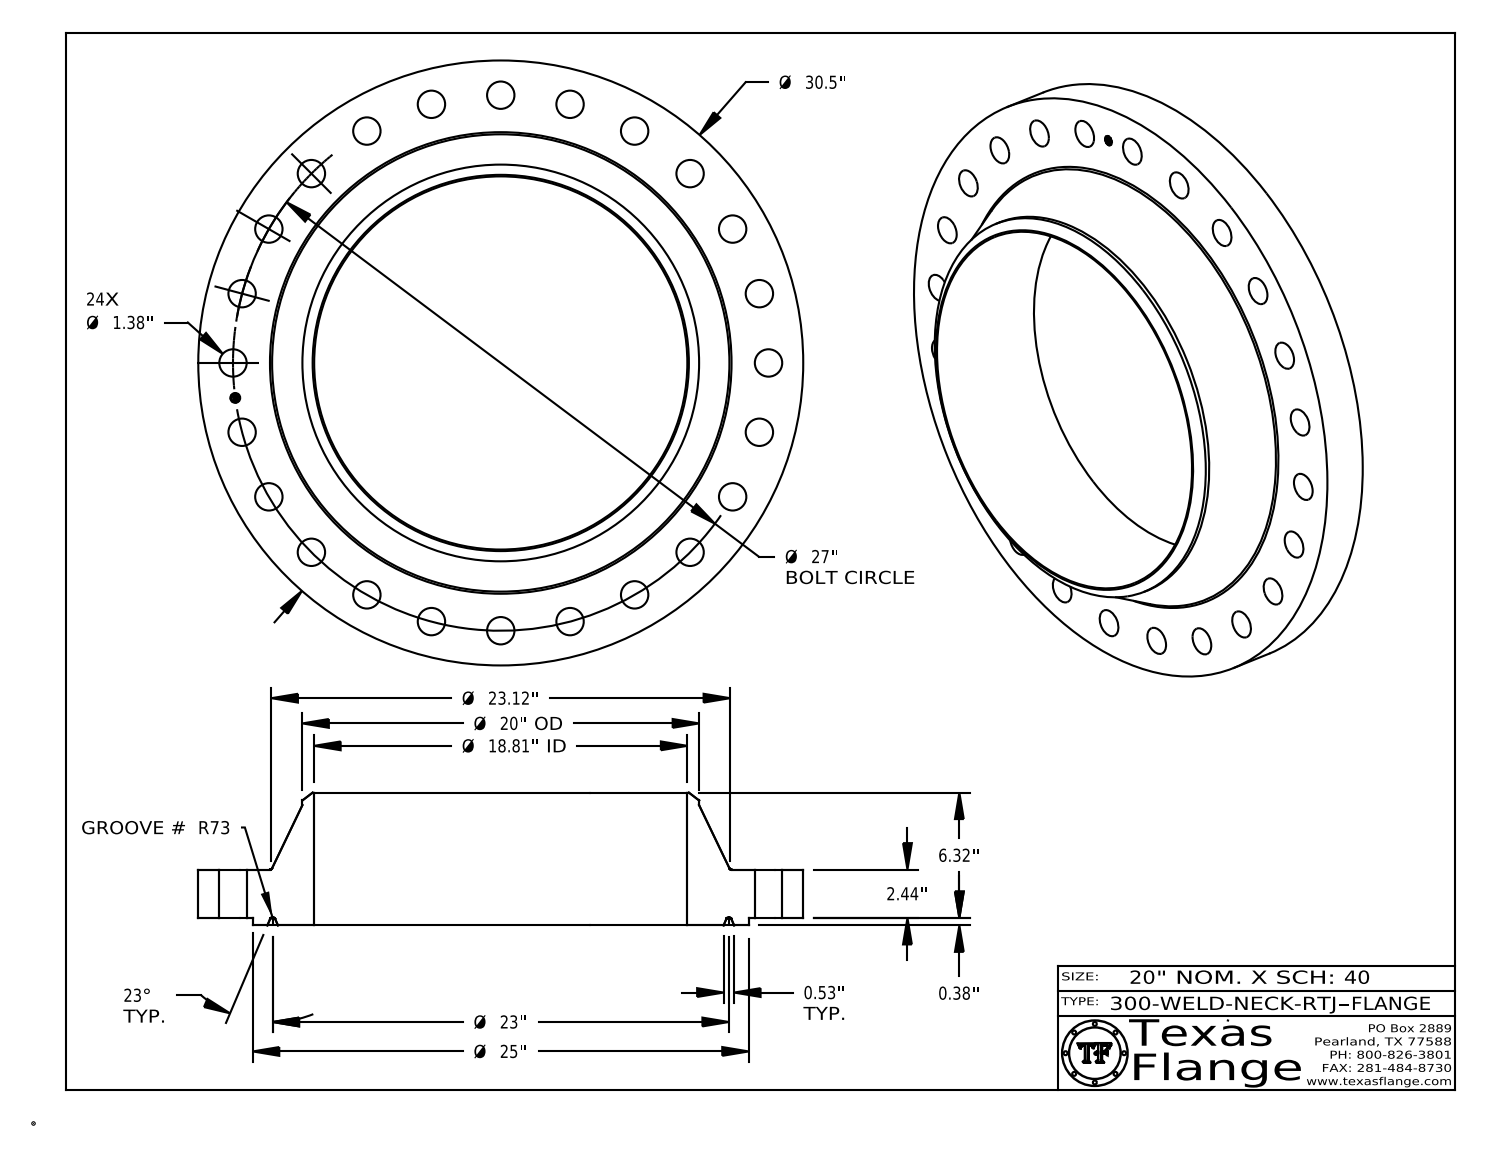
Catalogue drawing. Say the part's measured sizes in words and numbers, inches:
The part is named "300-WELD-NECK-RTJ". Its 3-D file was written by "CATIA V5 STEP AP214 (AUTOMOTIVE_DESIGN)". It is 1 solid with 461 faces: 371 planar, 76 cylindrical and 14 other. Overall it measures 30.5 by 30.5 by 6.695 inches. Its volume is 1 389 cubic inches and its surface area 1 941 square inches. Round holes: 24 of diameter 1.38, 1 of diameter 0.495, 1 of diameter 18.812. Round bosses or shafts: 8 of diameter 0.03, 1 of diameter 30.5, 1 of diameter 25, 1 of diameter 20, 1 of diameter 0.39. The main face-to-face distances are 2.44, 0.375, 2.815, 6.695, 6.32, 3.88, 2.8, 2.425, 0.015, 3.895. The hole center spacings are 13.5, 3.524, 6.988, 10.333, 16.437, 24.945, 26.769, 21.421.
